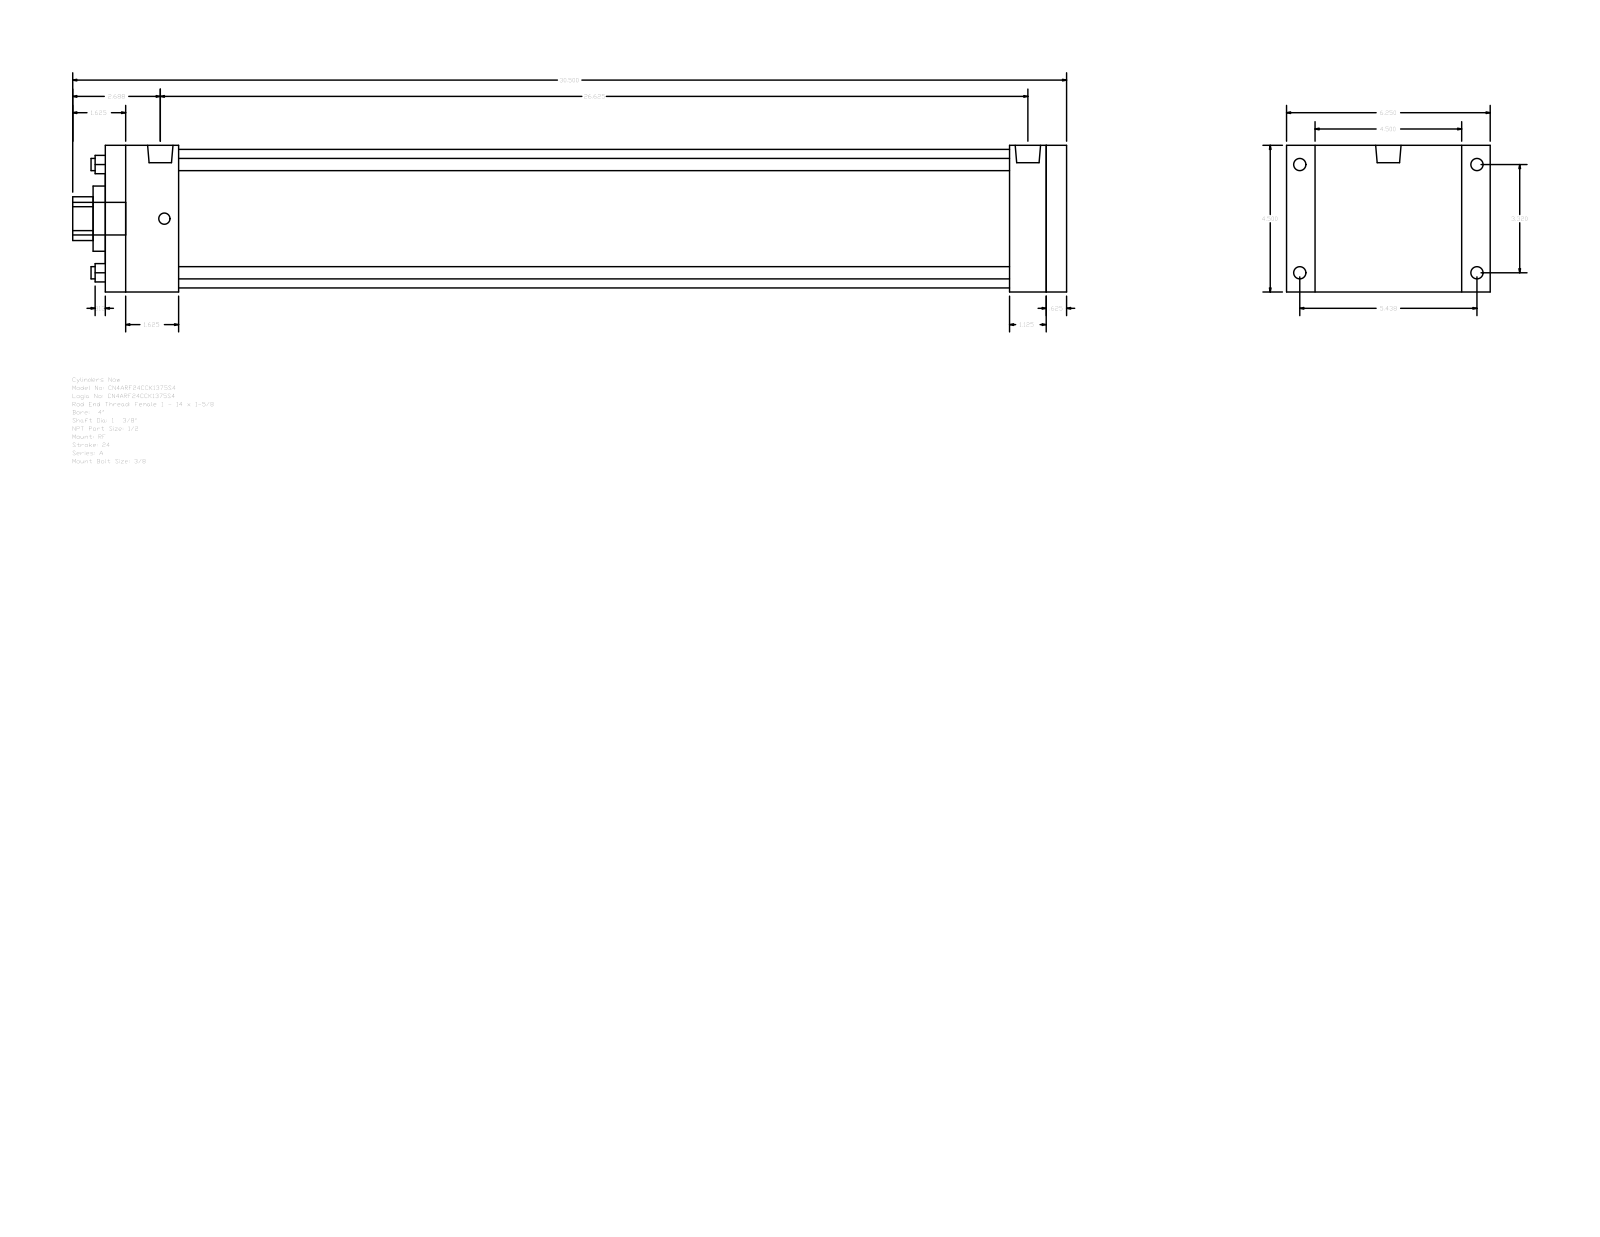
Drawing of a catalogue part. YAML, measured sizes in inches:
part_name: "A_RF__0400_1.375"
step_written_by: "GSSL Pune (CONFIG_CONTROL_DESIGN)"
units: inches
bodies: {solids: 0, faces: 92, planar: 64, cylindrical: 28, other: 0}
overall_size: [30.5, 6.25, 4.5]
round_holes:
  - {diameter: 0.375, count: 4}
  - {diameter: 1.375, count: 1}
  - {diameter: 2, count: 1}
  - {diameter: 4.25, count: 1}
round_bosses_or_shafts:
  - {diameter: 0.375, count: 4}
  - {diameter: 0.344, count: 4}
  - {diameter: 0.778, count: 2}
  - {diameter: 1, count: 1}
partial_cylinders:
  - {radius: 0.672, count: 1}
face_to_face_distances: [4.5, 29.5, 0.625, 28.875, 1.125, 0.875, 5.375, 27.75, 1.75, 2.25]
hole_center_spacings: [2.347, 3.32, 4.695]
